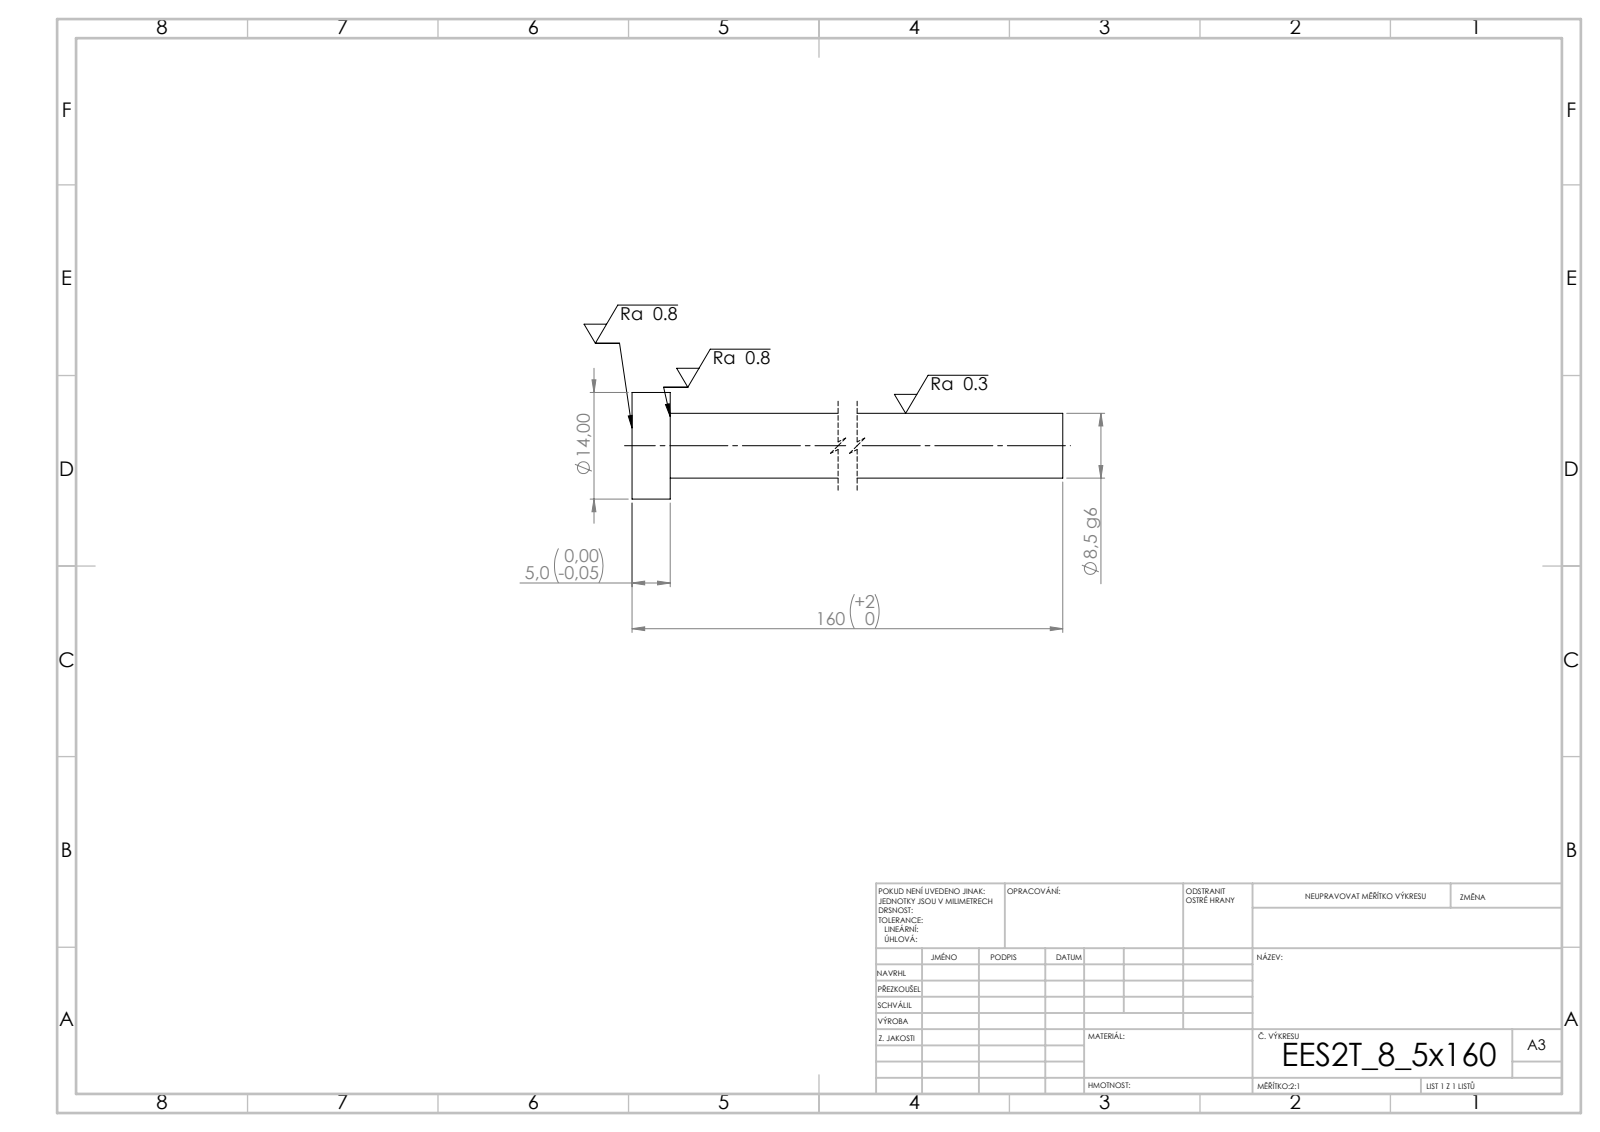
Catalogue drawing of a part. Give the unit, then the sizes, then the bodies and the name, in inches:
Units: inches
Overall size (bounding box): 6.299 × 0.551 × 0.551
Round bosses / shafts (diameter × count): ⌀0.551 ×1, ⌀0.335 ×1
Main face-to-face distances: 0.197, 6.299, 6.102
Volume: 0.584 in³ · Surface area: 7.234 in²
Bodies: 1 solid, 7 faces (3 planar, 4 cylindrical, 0 other)
STEP written by: SolidWorks 2019 (CONFIG_CONTROL_DESIGN)
